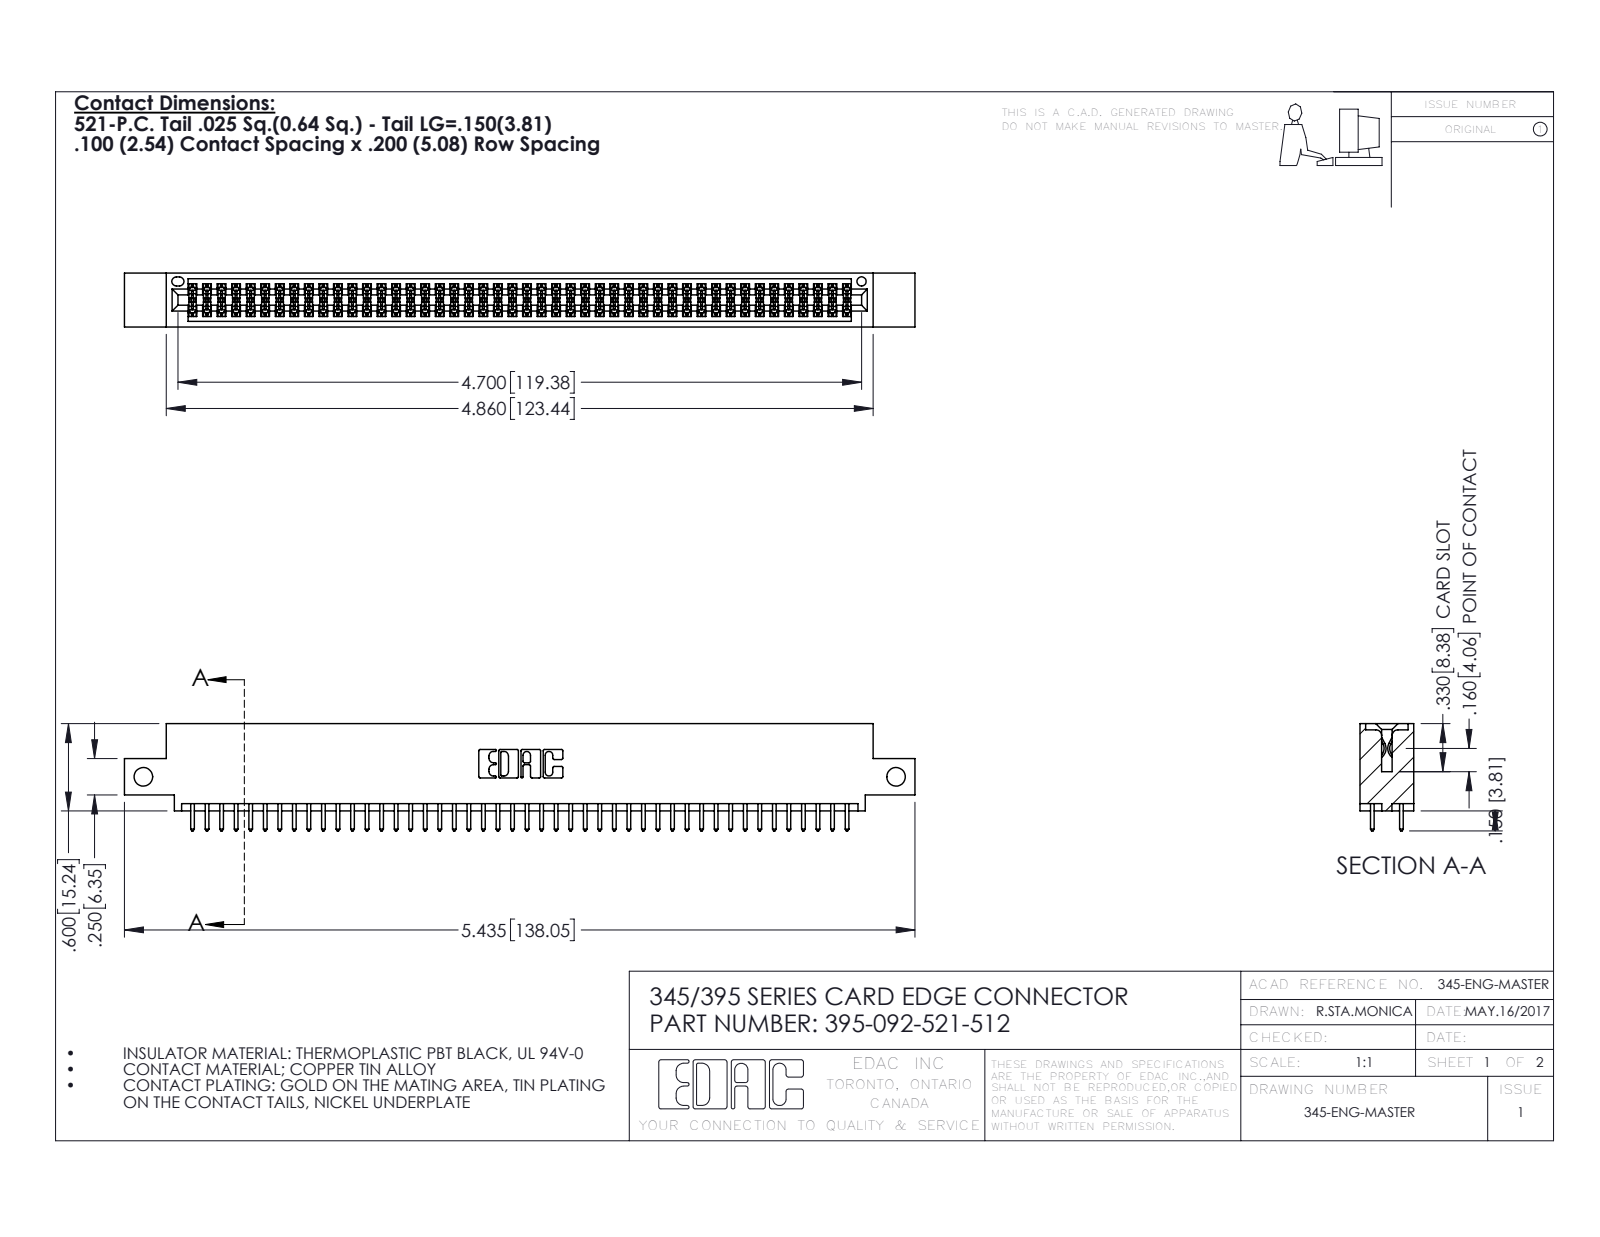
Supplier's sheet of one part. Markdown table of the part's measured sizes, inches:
| quantity | value |
| --- | --- |
| part name | 395-092-521-512; 345-292-001_345-293-121; 345 Part_0.110 Offset - Side Mount |
| STEP written by | SolidWorks 2016 (CONFIG_CONTROL_DESIGN) |
| units | inches |
| bodies | 93 solids, 4730 faces (3120 planar, 1610 cylindrical, 0 other) |
| overall size | 5.435 × 0.737 × 0.37 |
| volume | 0.809 in³ |
| surface area | 30.03 in² |
| round holes (diameter × count) | 0.128 × 2, 0.064 × 1 |
| partial cylindrical surfaces (radius × count) | 0.006 × 138, 0.01 × 92, 0.01 × 22, 0.007 × 6, 0.031 × 6, 0.026 × 3, 0.014 × 2, 0.019 × 2 |
| main face-to-face distances | 0.298, 0.072, 0.2, 0.37, 0.098, 0.272, 0.025, 0.225, 0.175, 0.149 |
| hole center spacings | 5.175 |
